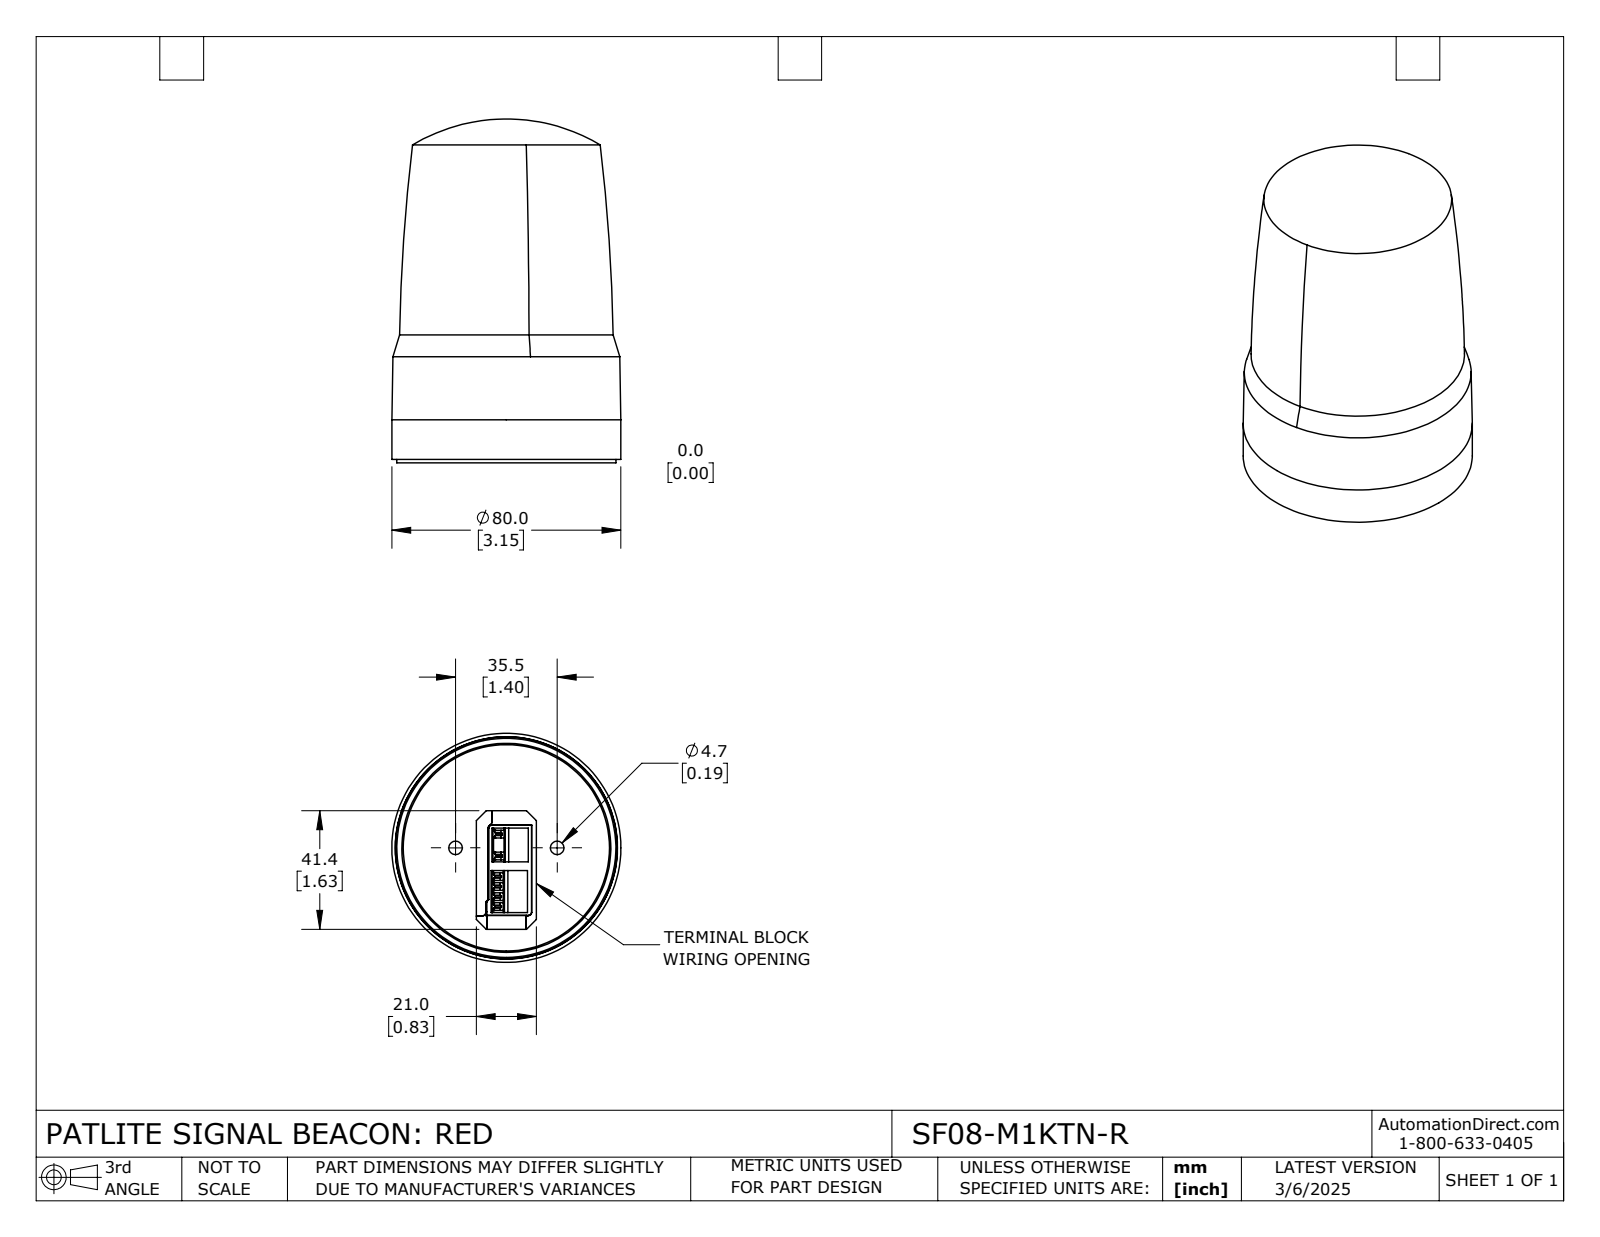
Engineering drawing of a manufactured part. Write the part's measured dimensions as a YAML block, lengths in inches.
part_name: "SF08-M1KTN-R"
step_written_by: "SolidWorks 2024 (CONFIG_CONTROL_DESIGN)"
units: inches
bodies: {solids: 2, faces: 287, planar: 199, cylindrical: 23, other: 65}
overall_size: [4.724, 3.15, 3.15]
volume: 29.01
surface_area: 81.21
round_holes:
  - {diameter: 0.185, count: 2}
  - {diameter: 0.48, count: 2}
  - {diameter: 2.874, count: 1}
round_bosses_or_shafts:
  - {diameter: 3.15, count: 1}
  - {diameter: 3.012, count: 1}
  - {diameter: 2.937, count: 1}
  - {diameter: 2.835, count: 1}
partial_cylinders:
  - {radius: 1.319, count: 1}
  - {radius: 1.362, count: 1}
face_to_face_distances: [0.248, 0.185, 0.433, 0.071, 0.504, 0.256, 0.059, 0.374, 0.126, 0.13]
hole_center_spacings: [0.699, 1.398]
